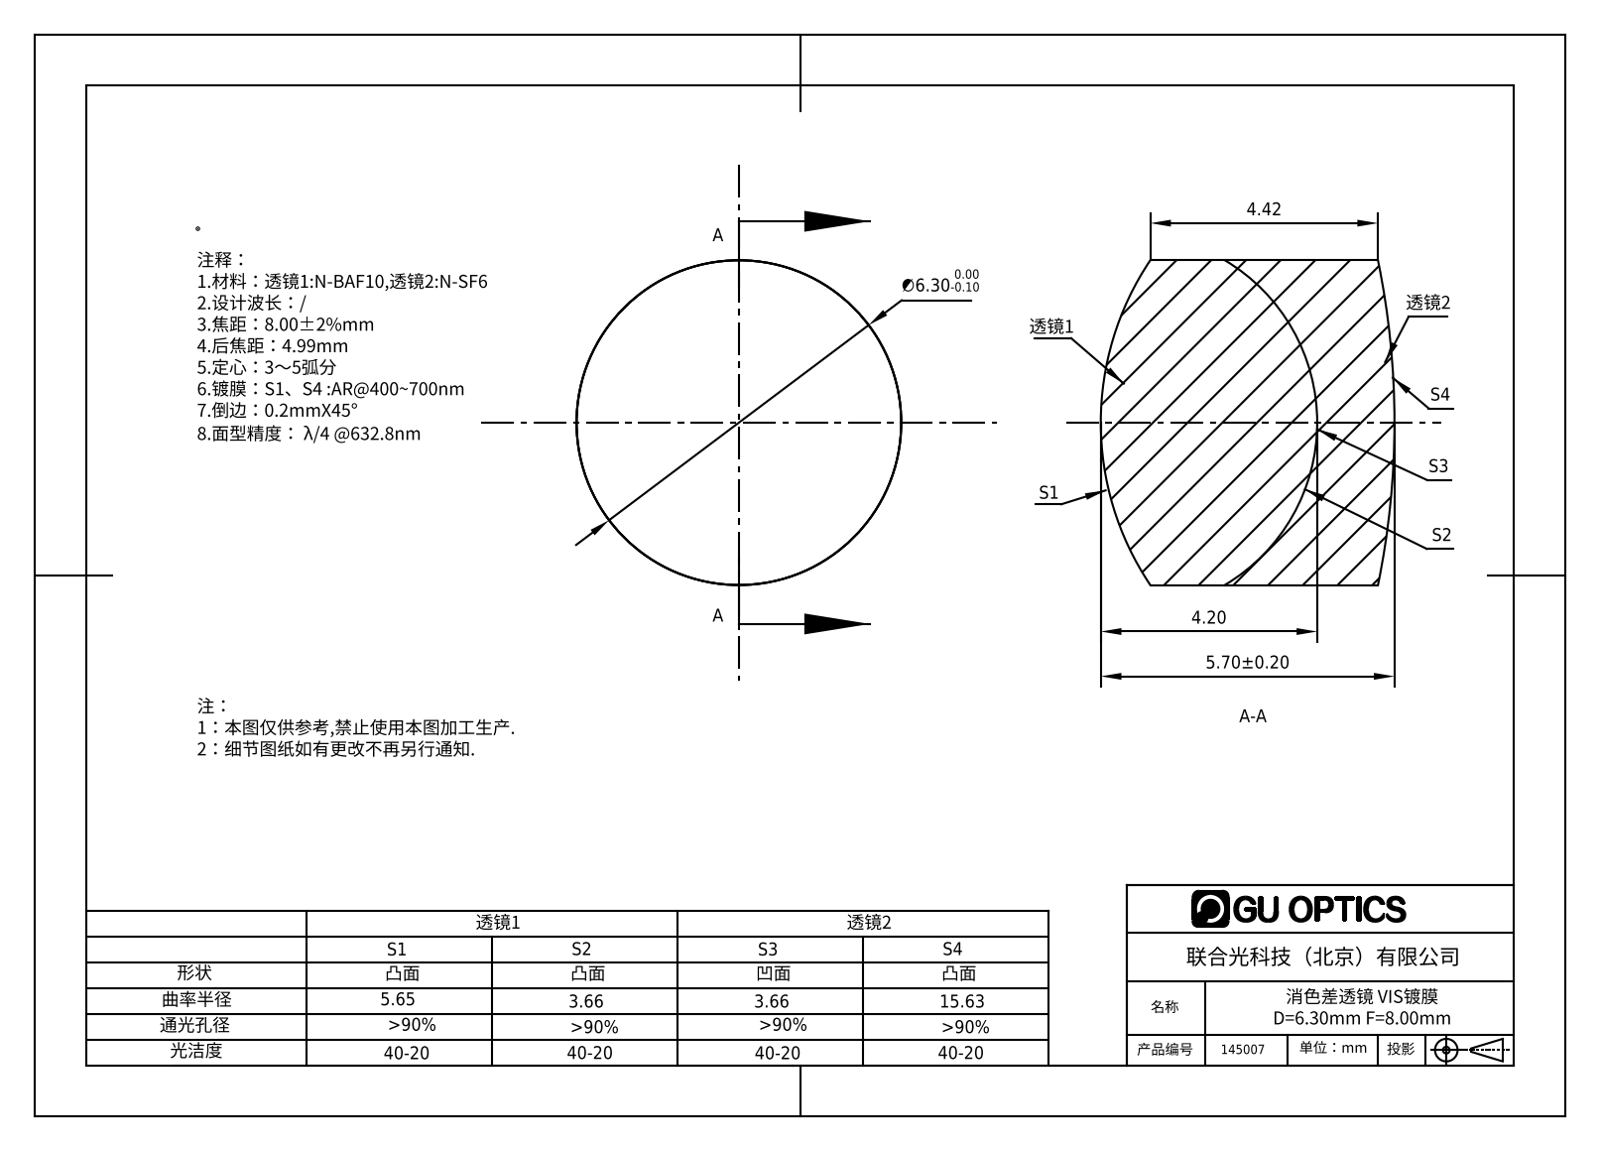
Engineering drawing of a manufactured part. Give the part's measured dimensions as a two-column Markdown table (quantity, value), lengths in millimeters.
| quantity | value |
| --- | --- |
| part name | 145007 |
| STEP written by | SolidWorks 2016 (AUTOMOTIVE_DESIGN) |
| units | millimeters |
| bodies | 2 solids, 12 faces (0 planar, 4 cylindrical, 8 other) |
| overall size | 6.3 × 6.3 × 5.7 |
| volume | 158 mm³ |
| surface area | 236 mm² |
| round bosses / shafts (diameter × count) | 6.3 × 1 |
